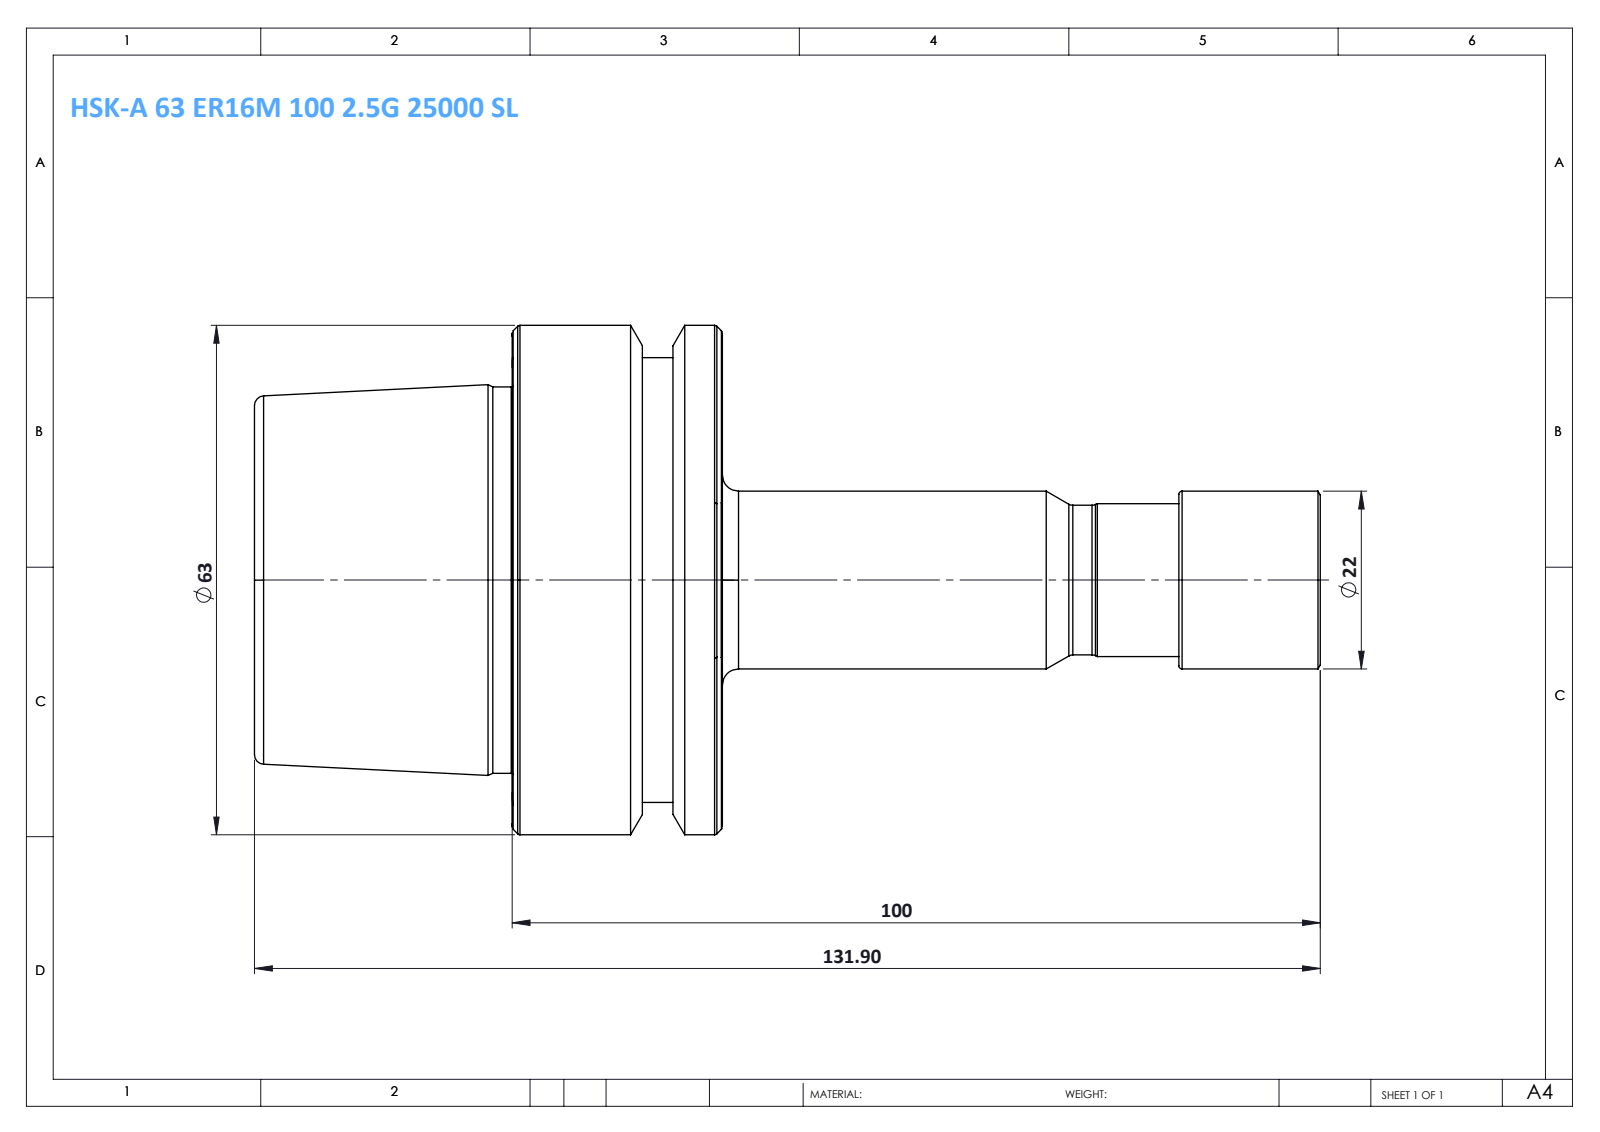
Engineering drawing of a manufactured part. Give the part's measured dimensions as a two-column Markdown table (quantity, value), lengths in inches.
| quantity | value |
| --- | --- |
| part name | HSK-A 63 ER16M 100 2.5G 25000 SL |
| STEP written by | SolidWorks 2014 (CONFIG_CONTROL_DESIGN) |
| units | inches |
| bodies | 1 solid, 84 faces (13 planar, 16 cylindrical, 55 other) |
| overall size | 5.193 × 2.48 × 2.48 |
| volume | 9.718 in³ |
| surface area | 33.58 in² |
| round bosses / shafts (diameter × count) | 2.48 × 1, 2.165 × 1, 1.881 × 1, 0.866 × 1, 0.744 × 1, 0.728 × 1 |
| main face-to-face distances | 2.28, 1.024, 1.256, 2.913, 3.937, 5.193, 3.303, 0.39, 0.634, 1.89 |
